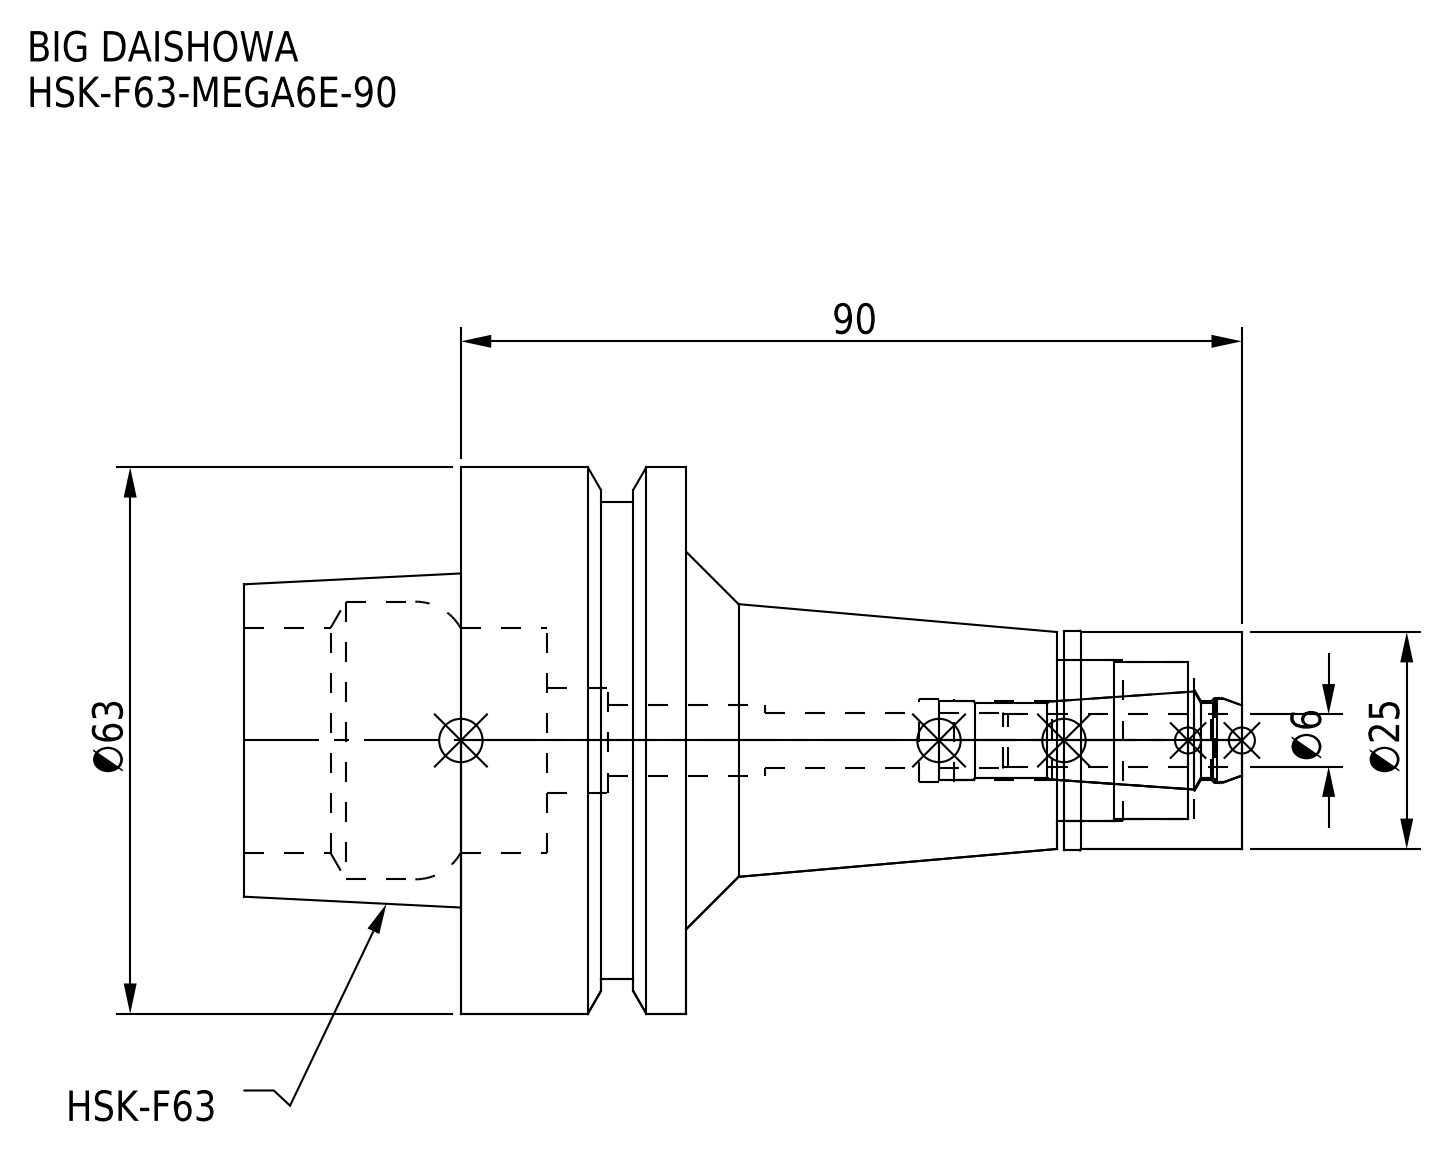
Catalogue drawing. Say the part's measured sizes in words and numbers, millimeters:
The part is named "HF63ME06090-060_ASM.stp; HSK-F63-MEGA6E-90-060-FreeParts; DXF_TEMP_ASSY_ASM_4_ASM.stp; MEN6_1.stp (+3 more)". Its 3-D file was written by "SolidWorks 2019 (CONFIG_CONTROL_DESIGN)". It is 2 solids with 81 faces: 17 planar, 40 cylindrical and 24 other. Overall it measures 115 by 63 by 63 millimeters. Its volume is 117 629 cubic millimeters and its surface area 28 047 square millimeters. Round holes: 1 of diameter 6.4, 1 of diameter 8.25, 1 of diameter 9, 1 of diameter 9.6, 1 of diameter 9.9, 1 of diameter 12, 1 of diameter 18, 1 of diameter 18.5, 1 of diameter 26, 1 of diameter 32. Round bosses or shafts: 1 of diameter 63, 1 of diameter 55, 1 of diameter 25.3, 1 of diameter 25. The main face-to-face distances are 26, 51, 25, 64, 90, 115, 80.05, 16.05, 9.95, 34.95.
